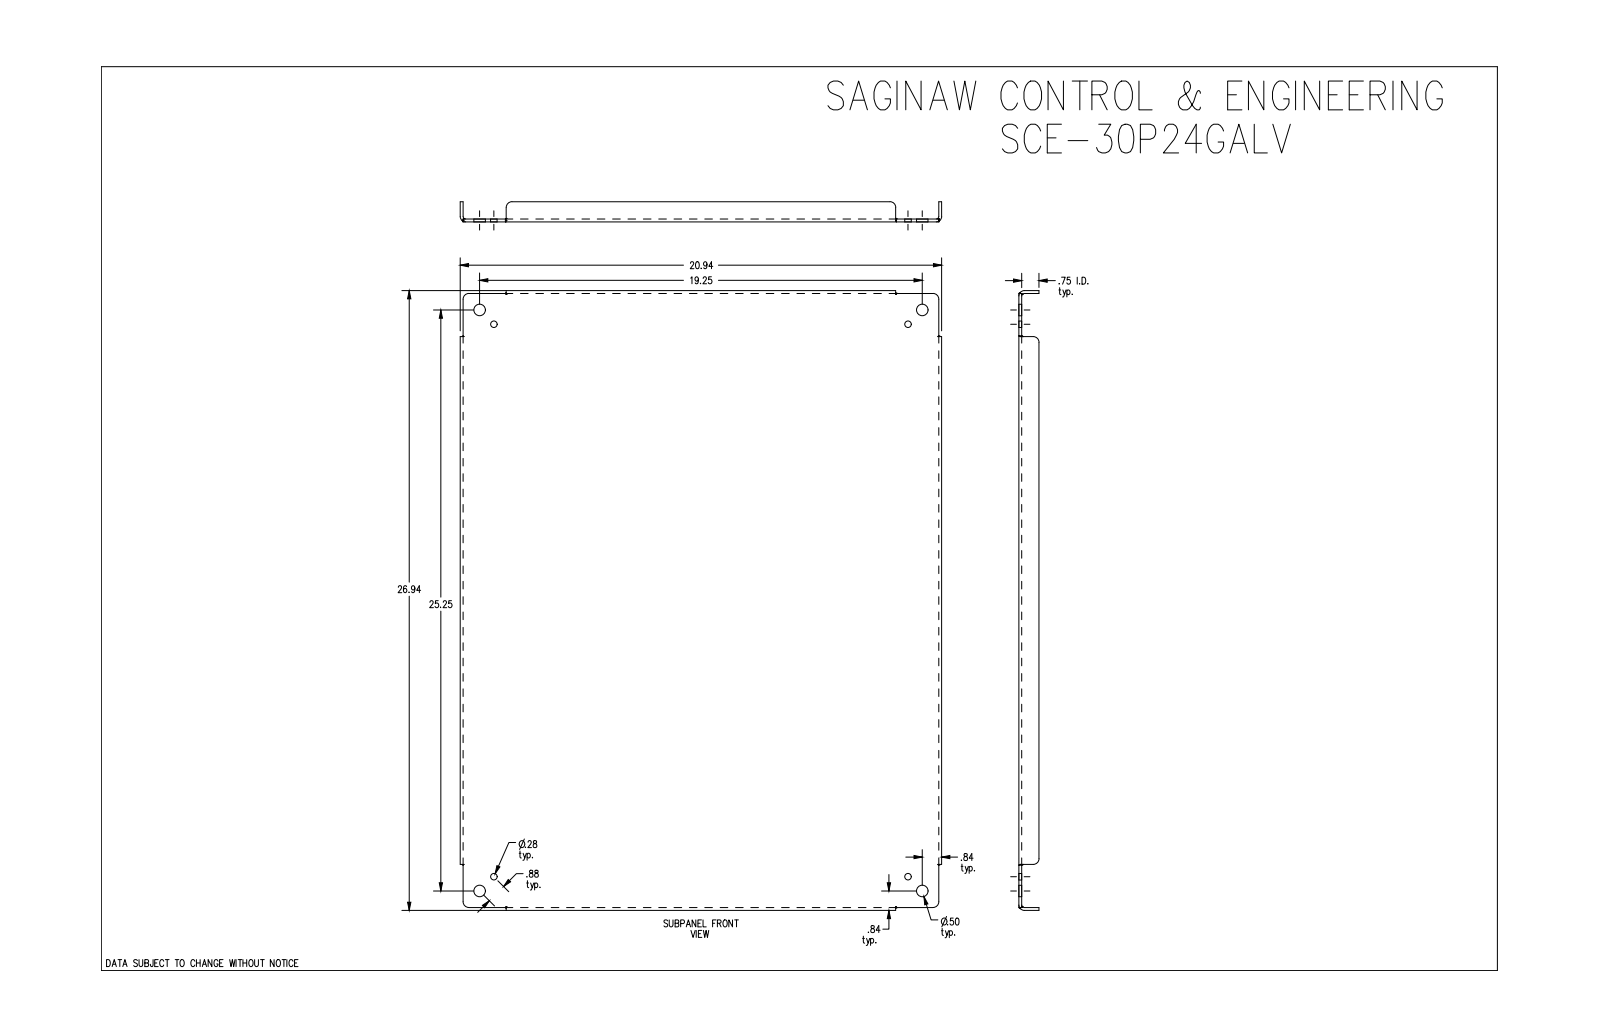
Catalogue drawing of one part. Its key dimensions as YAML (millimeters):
part_name: "SCE-30P24GALV"
step_written_by: "SolidWorks 2019 (CONFIG_CONTROL_DESIGN)"
units: millimeters
bodies: {solids: 1, faces: 82, planar: 30, cylindrical: 28, other: 24}
overall_size: [684.2, 531.8, 22.2]
volume: 1259000
surface_area: 801900
round_holes:
  - {diameter: 7.1, count: 4}
  - {diameter: 12.7, count: 4}
partial_cylinders:
  - {radius: 6.4, count: 8}
  - {radius: 2.8, count: 4}
  - {radius: 6, count: 4}
face_to_face_distances: [3.2, 3.2, 528.7, 681.1, 525.4, 531.8, 677.8, 684.2, 19.1, 22.2]
hole_center_spacings: [22.2, 473.5, 625.8, 784.5, 457.5, 489, 609.9, 641.4]
